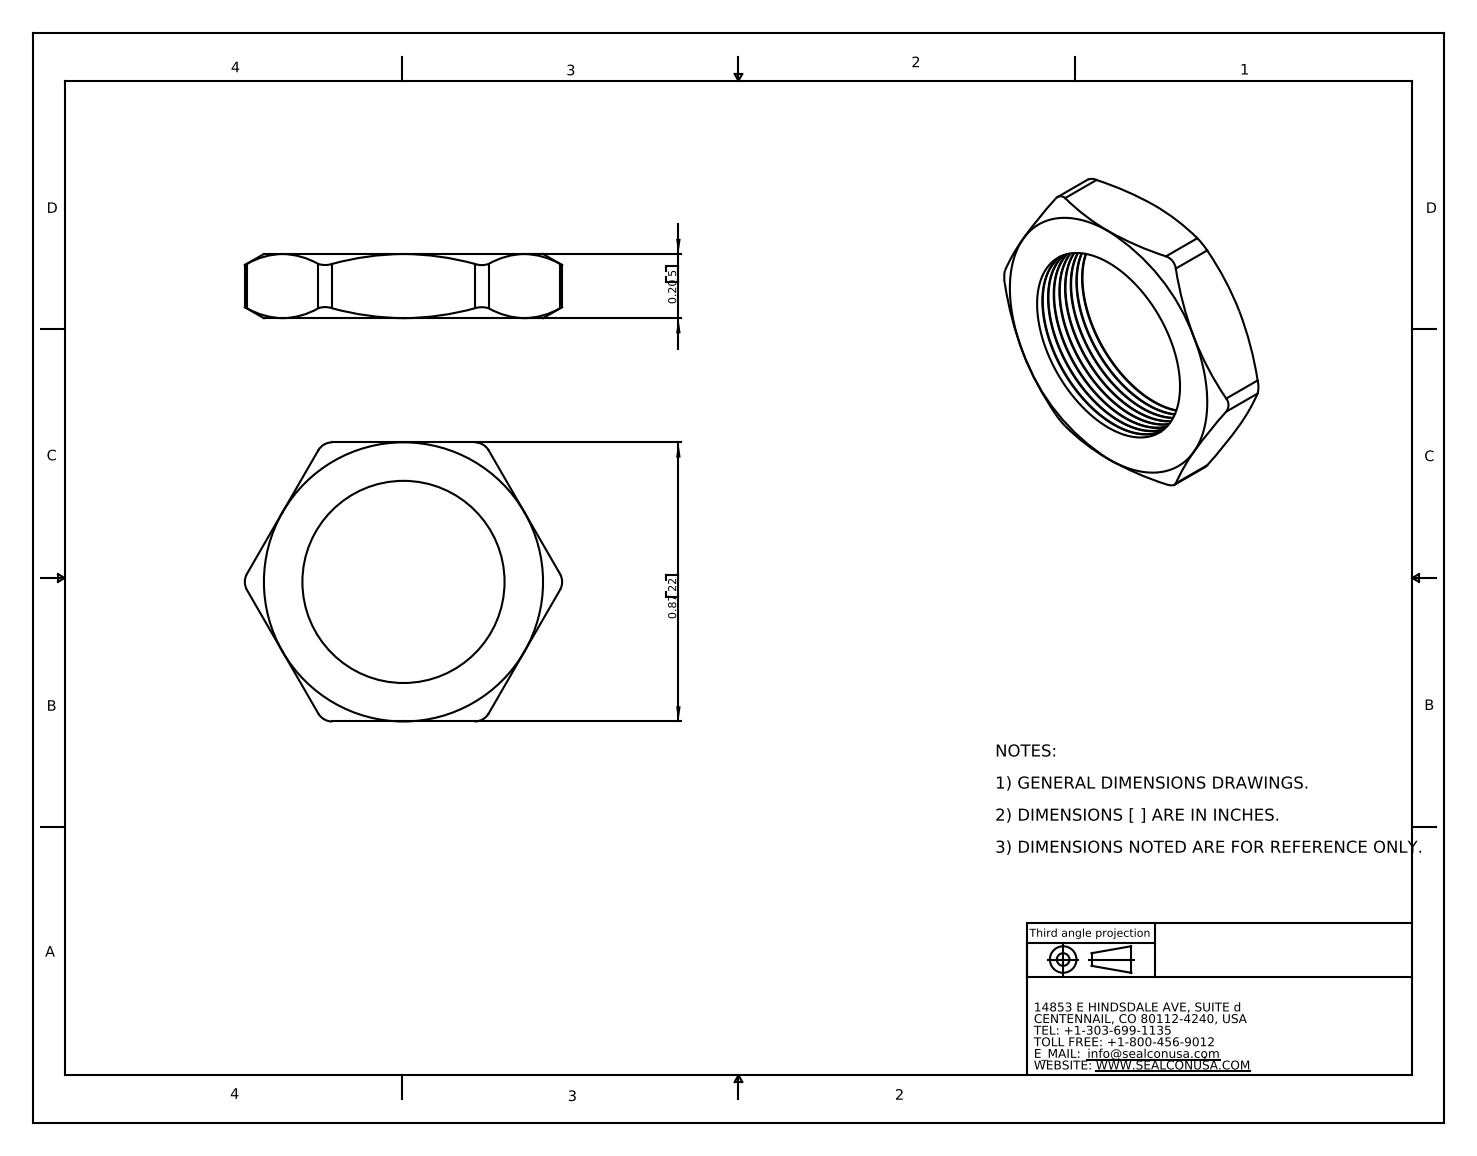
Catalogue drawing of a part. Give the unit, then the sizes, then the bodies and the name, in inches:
Units: inches
Overall size (bounding box): 0.989 × 0.87 × 0.2
Round holes (diameter × count): ⌀0.63 ×1
Partial cylindrical surfaces — rounded edges, fillets, slot ends (radius × count): R0.05 ×6
Main face-to-face distances: 0.2, 0.87
Volume: 0.063 in³ · Surface area: 2.008 in²
Bodies: 1 solid, 77 faces (8 planar, 23 cylindrical, 46 other)
Part name (STEP PRODUCT): NM-16-GY
STEP written by: SolidWorks 2007 (CONFIG_CONTROL_DESIGN)
